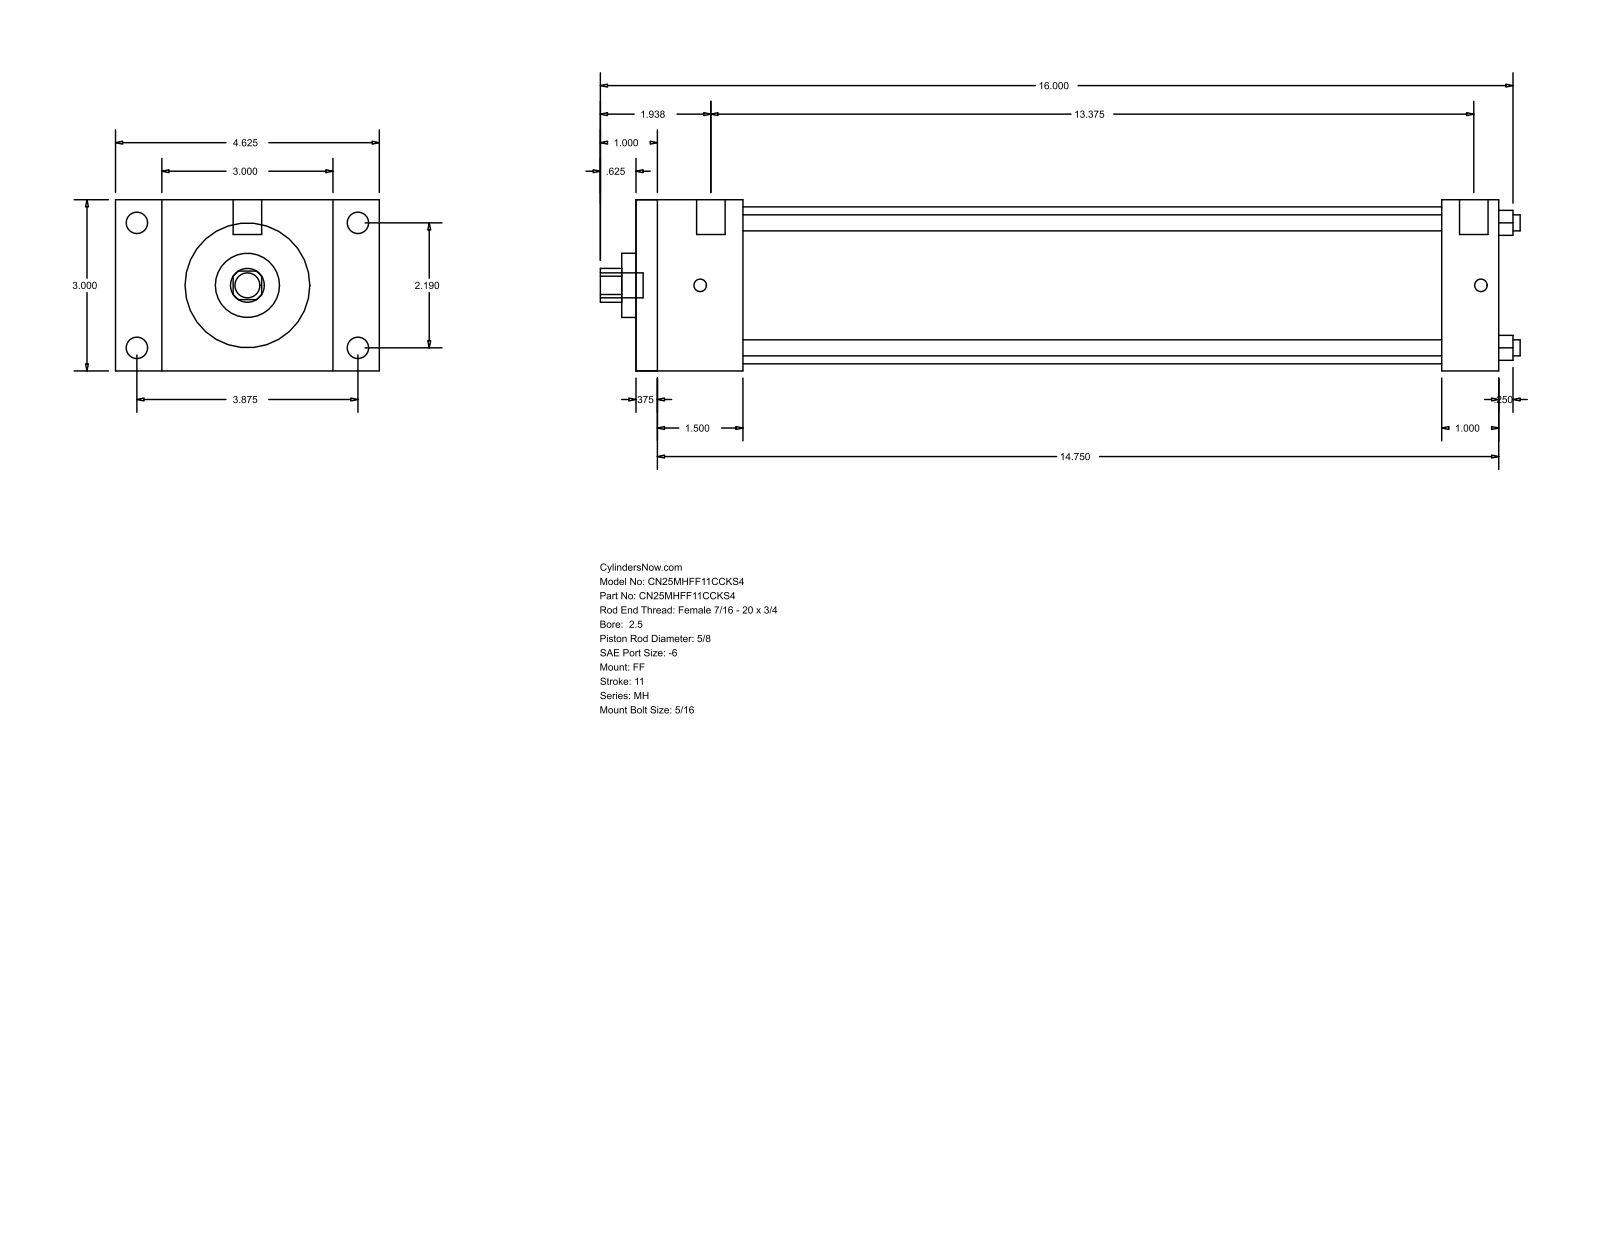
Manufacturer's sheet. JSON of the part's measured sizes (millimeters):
{"part_name": "MH_FF__0250_0.625", "step_written_by": "GSSL Pune (CONFIG_CONTROL_DESIGN)", "units": "millimeters", "bodies": {"solids": 0, "faces": 92, "planar": 64, "cylindrical": 28, "other": 0}, "overall_size": [409.57, 117.47, 76.2], "round_holes": [[7.14, 4], [15.88, 1], [28.57, 1], [69.85, 1]], "round_bosses_or_shafts": [[9.53, 4], [5.56, 4], [12.7, 2], [11.11, 1]], "partial_cylinders_radius": [[7.54, 1]], "face_to_face_distances": [76.2, 384.17, 9.52, 374.65, 25.4, 47.62, 358.77, 38.1, 349.25, 311.15], "hole_center_spacings": [39.33, 55.62, 78.66]}
